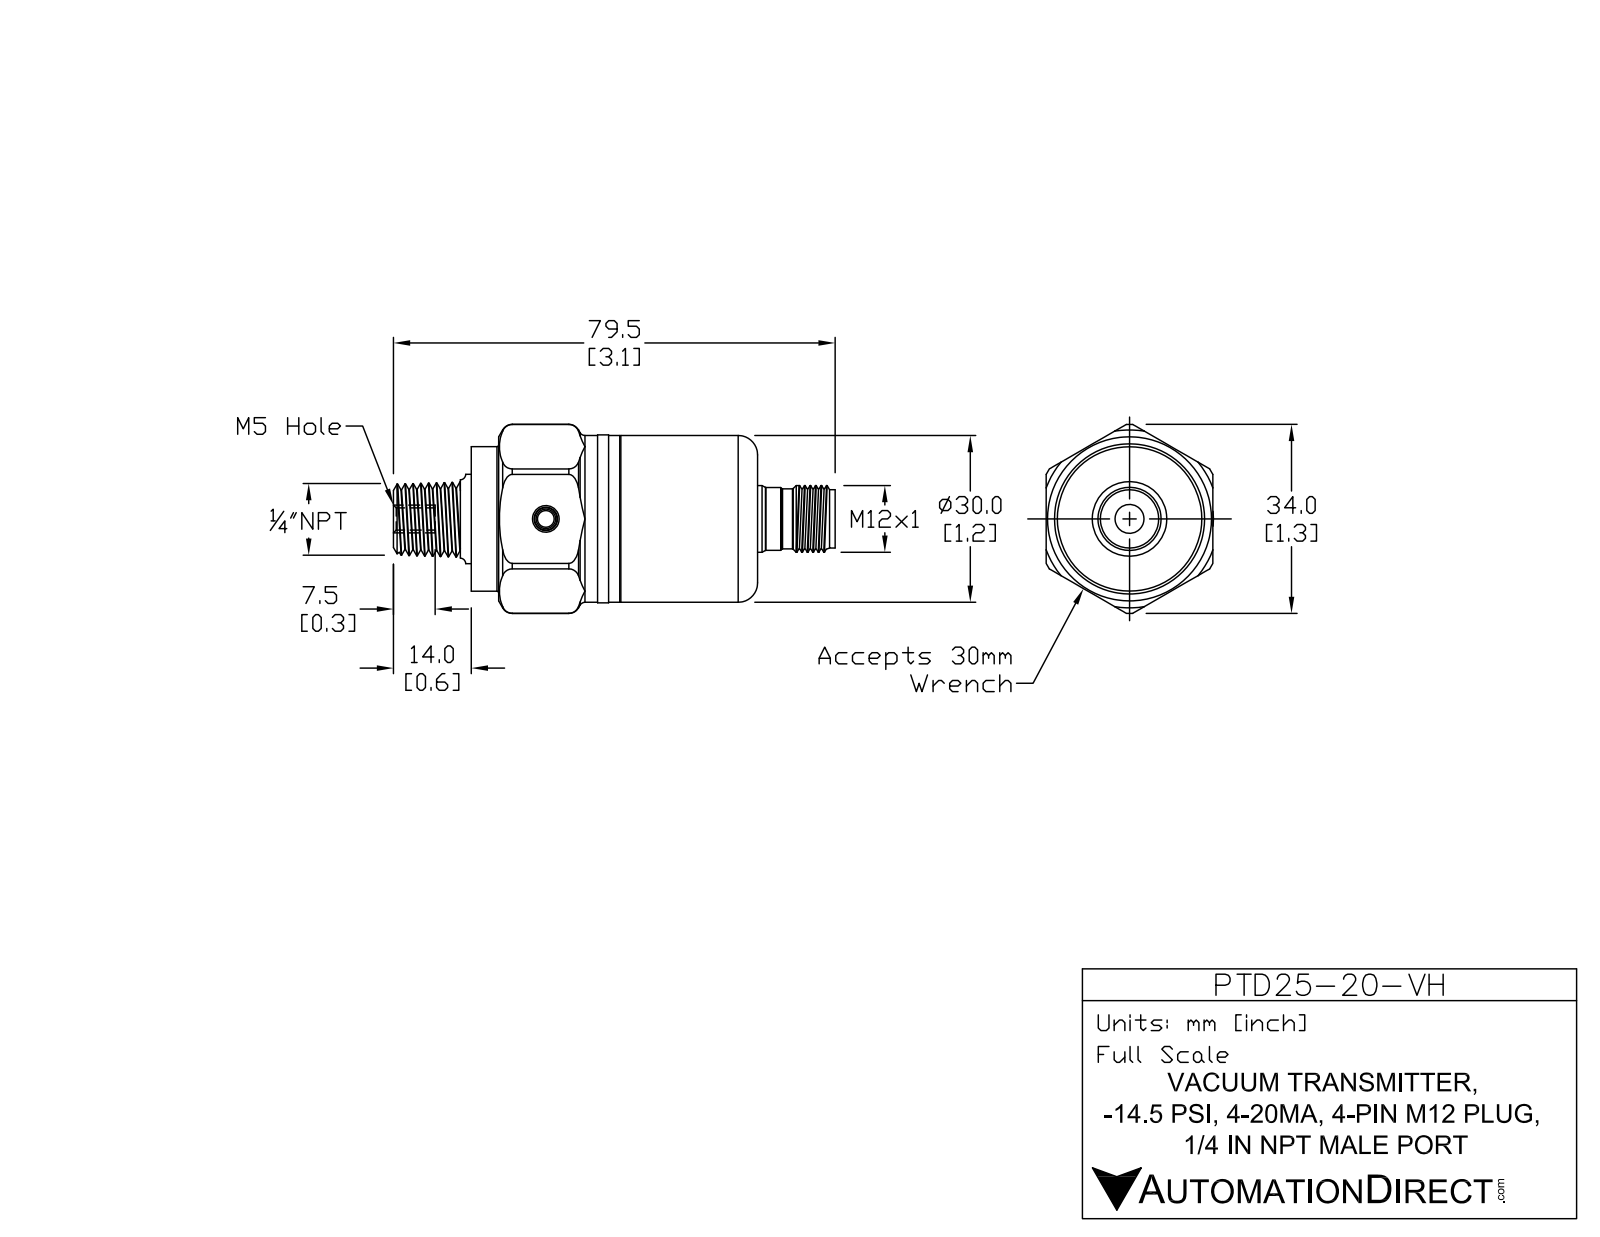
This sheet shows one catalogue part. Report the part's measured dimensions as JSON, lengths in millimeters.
{"part_name": "PTD25-20-VH", "step_written_by": "SolidWorks 2017 (AUTOMOTIVE_DESIGN)", "units": "millimeters", "bodies": {"solids": 1, "faces": 124, "planar": 36, "cylindrical": 59, "other": 29}, "overall_size": [79.5, 33.78, 31.7], "volume_mm3": 39212, "surface_area_mm2": 8088, "round_holes": [[4, 1], [8.5, 1]], "round_bosses_or_shafts": [[30.05, 1], [30, 1], [25.96, 1], [14, 1], [13.5, 1], [12, 1]], "partial_cylinders_radius": [[3.76, 1], [16.95, 1]], "face_to_face_distances": [51, 29.98, 30, 48, 3, 65, 17, 14, 30.01, 5.65]}
